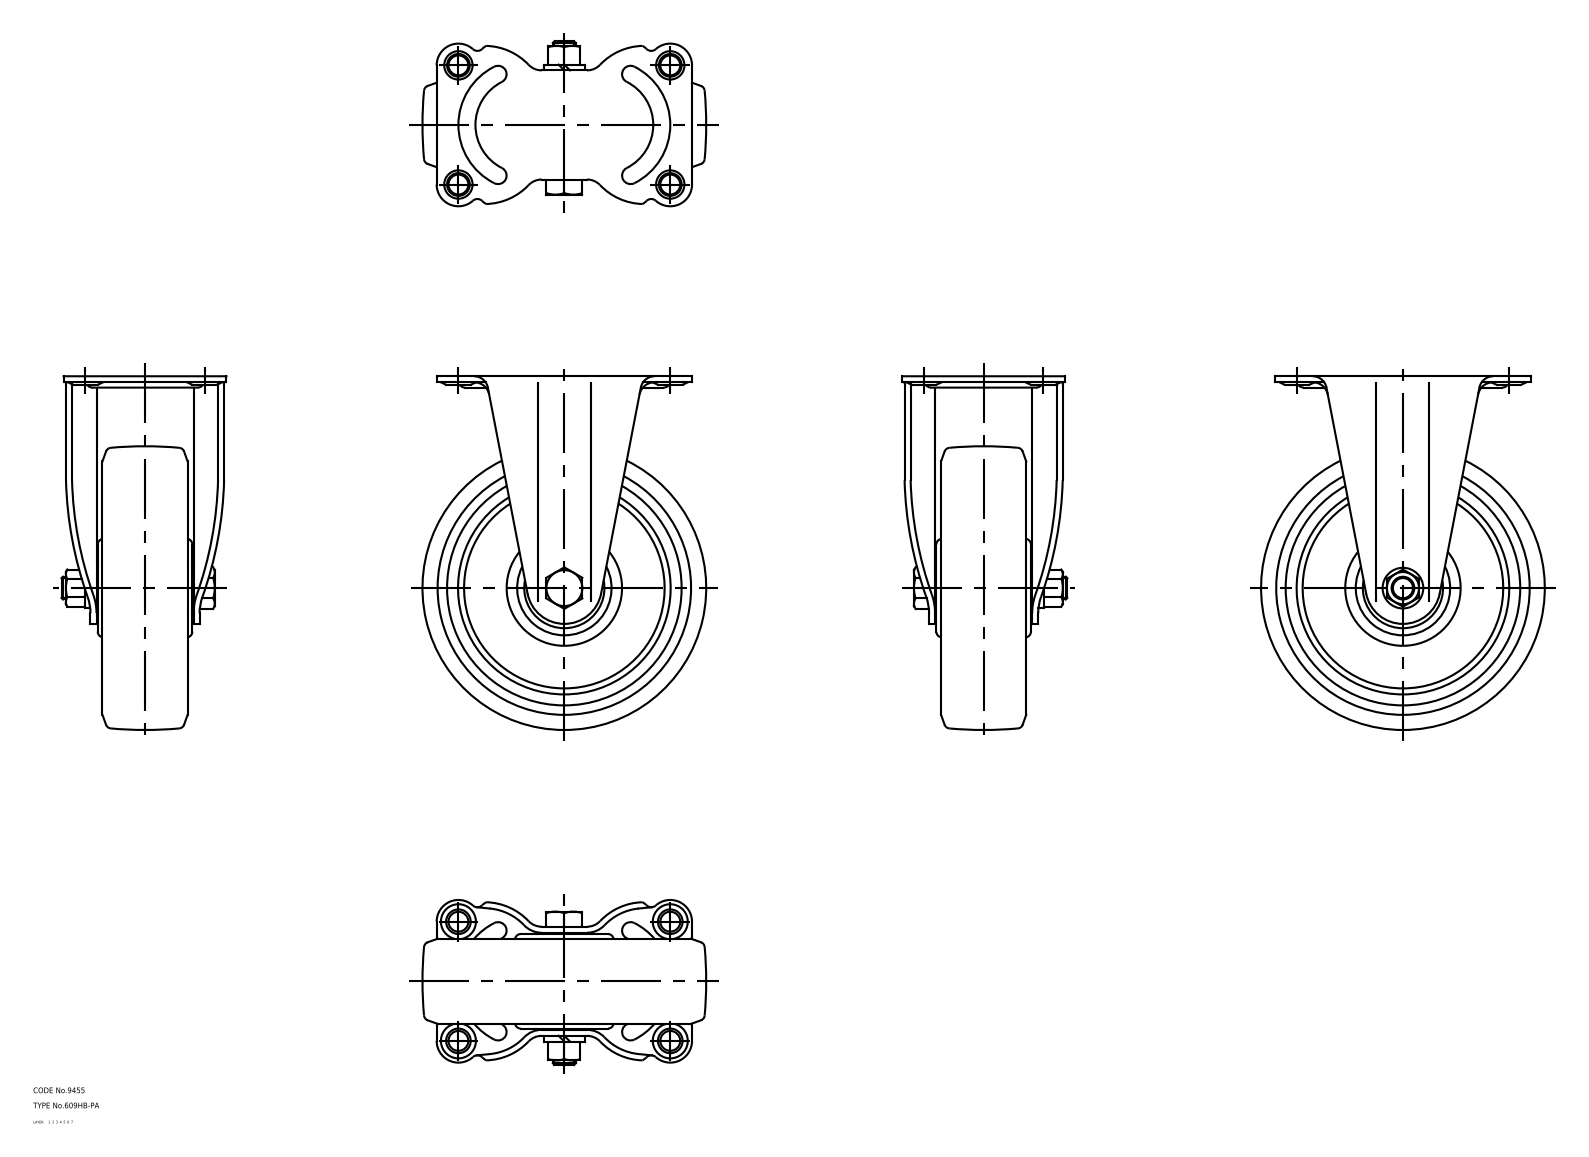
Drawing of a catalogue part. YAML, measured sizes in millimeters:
part_name: "67124338; 67124351; 67124364"
step_written_by: "CADfix (AUTOMOTIVE_DESIGN)"
units: millimeters
bodies: {solids: 3, faces: 208, planar: 0, cylindrical: 0, other: 208}
overall_size: [187, 150, 87.15]
volume: 776345
surface_area: 118678
